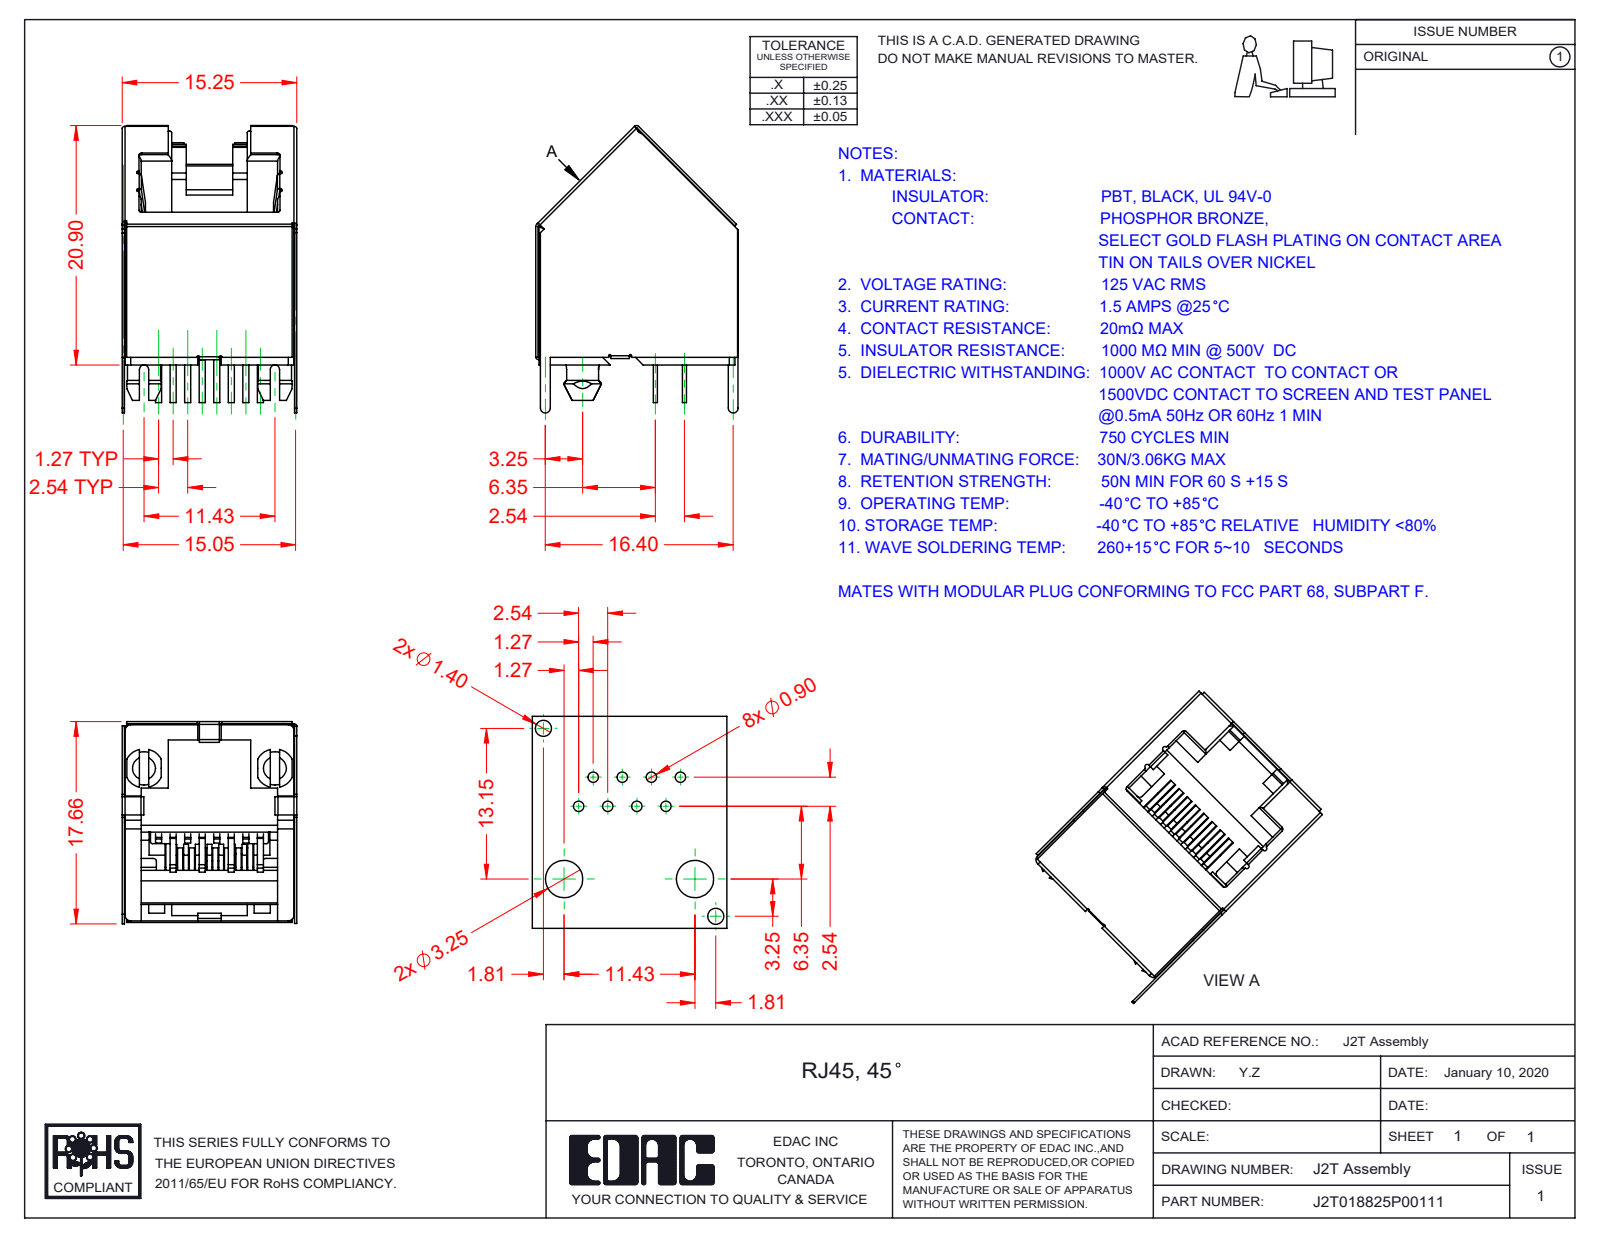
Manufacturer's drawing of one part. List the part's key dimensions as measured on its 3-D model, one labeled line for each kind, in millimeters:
Part name (STEP PRODUCT): 2T Shell; 2T Insulator; RJ2T018825P00111; 2T Contact Lock (+1 more)
STEP written by: SolidWorks 2016 (CONFIG_CONTROL_DESIGN)
Units: millimetres
Bodies: 11 solids, 631 faces (447 planar, 161 cylindrical, 23 other)
Overall size (bounding box): 25.09 × 17.66 × 15.25
Volume: 1 960 mm³ · Surface area: 5 178 mm²
Round bosses / shafts (diameter × count): ⌀2.9 ×2
Partial cylindrical surfaces — rounded edges, fillets, slot ends (radius × count): R0.5 ×21, R1 ×16, R0.2 ×12, R0.25 ×10, R1.46 ×8, R1.52 ×8, R0.1 ×5, R0.3 ×3
Main face-to-face distances: 15.04, 1.42, 13.33, 14.8, 15, 15.24, 14.84, 14.99, 14.79, 14.75
